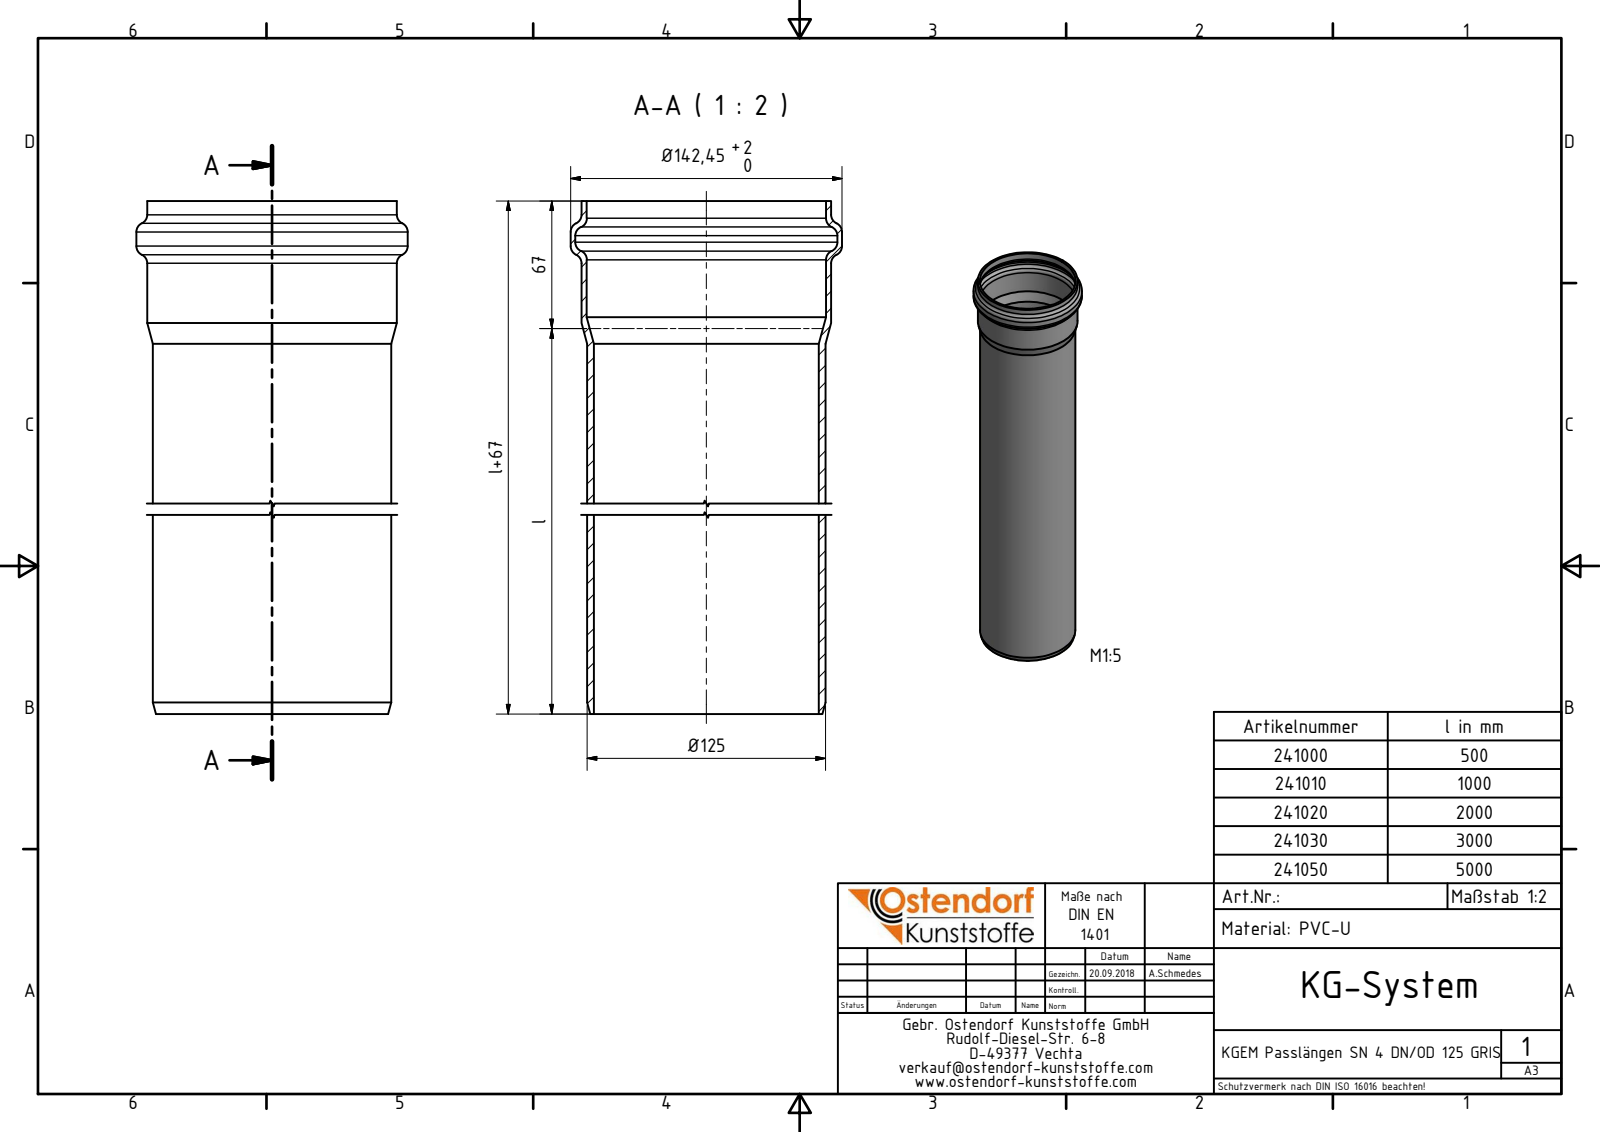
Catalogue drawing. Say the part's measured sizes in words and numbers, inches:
The part is named "241050 KGEM Passlängen SN 4 DN_OD 125x5000 GRIS". Its 3-D file was written by "Autodesk Inventor 2016 (AUTOMOTIVE_DESIGN)". It is 1 solid with 21 faces: 2 planar, 8 cylindrical and 11 other. Overall it measures 199.488 by 5.608 by 5.608 inches. Its volume is 413.1 cubic inches and its surface area 6 019 square inches. Round holes: 1 of diameter 4.652, 1 of diameter 4.947, 1 of diameter 5.419. Round bosses or shafts: 1 of diameter 5.608, 1 of diameter 5.159, 1 of diameter 4.927. The main face-to-face distances are 199.488.
